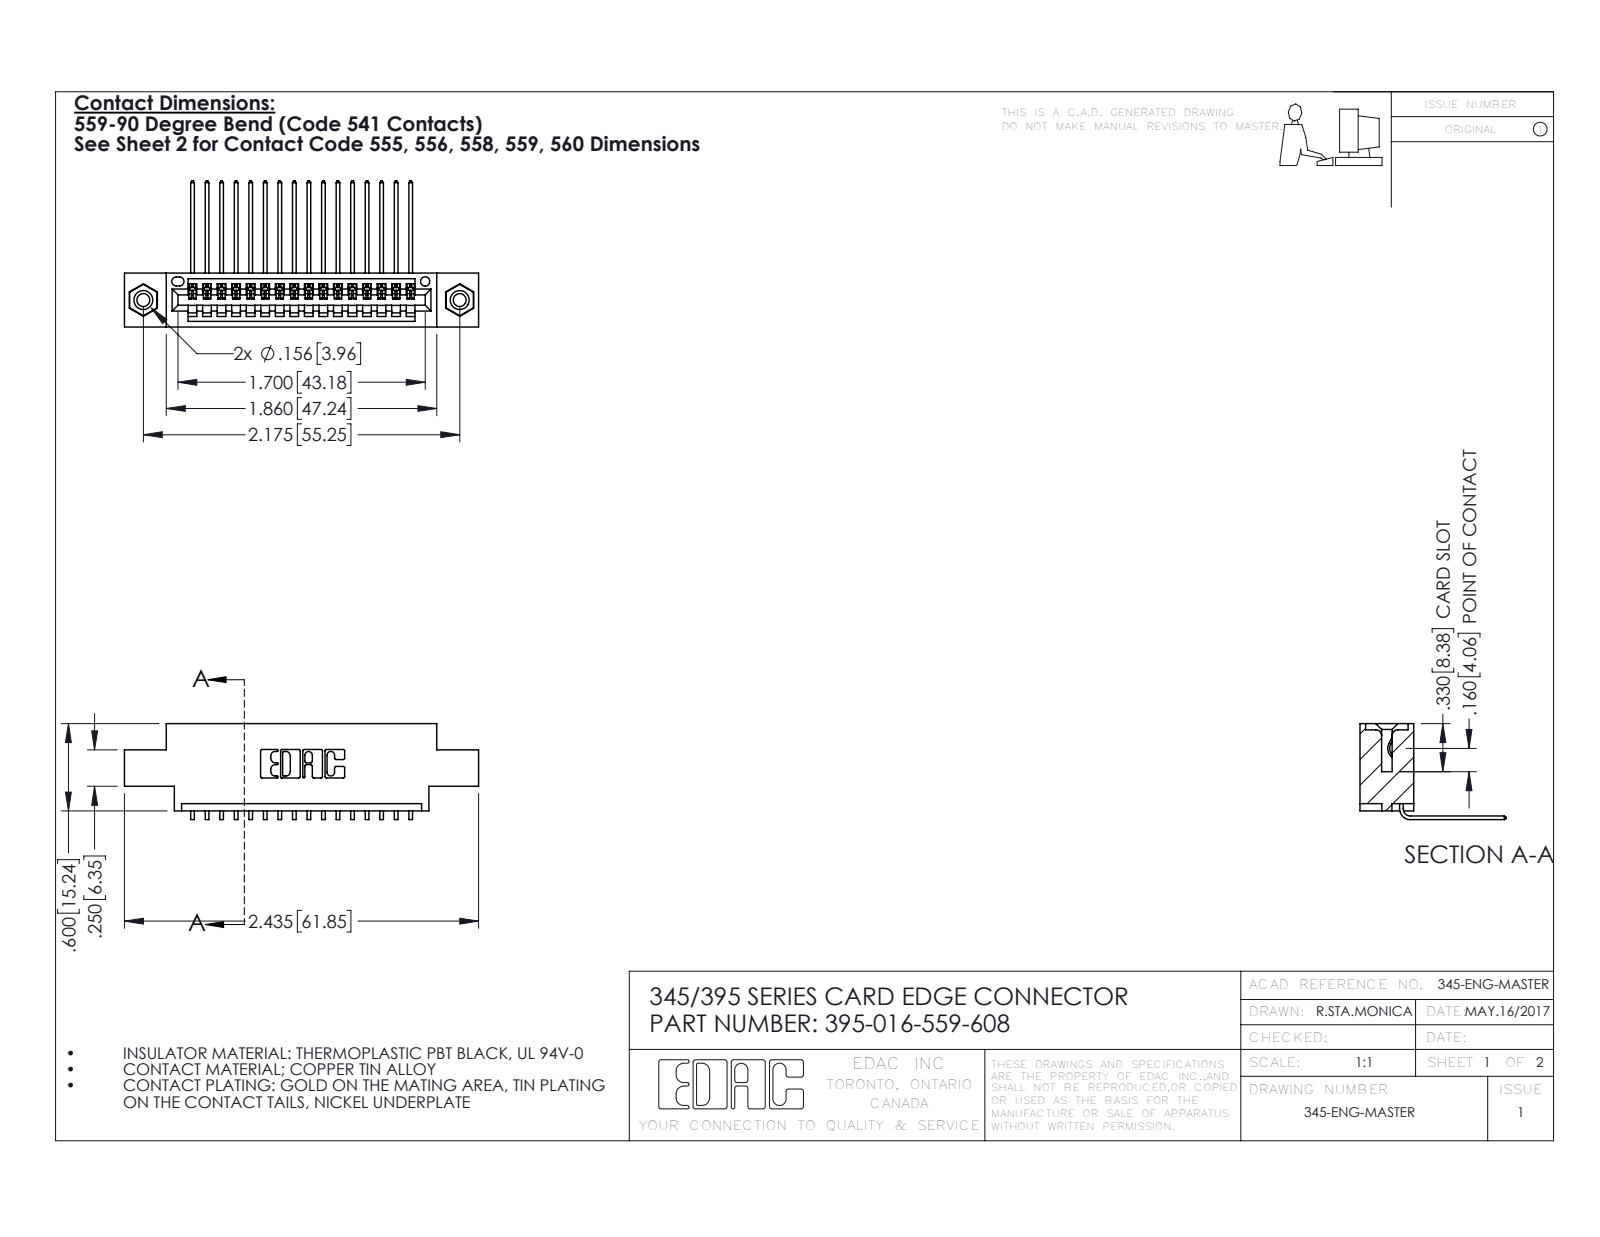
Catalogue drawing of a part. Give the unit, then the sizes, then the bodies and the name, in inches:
Units: inches
Overall size (bounding box): 2.435 × 1.005 × 0.659
Round holes (diameter × count): ⌀0.089 ×2, ⌀0.125 ×2, ⌀0.156 ×2, ⌀0.064 ×1
Round bosses / shafts (diameter × count): ⌀0.155 ×2
Partial cylindrical surfaces — rounded edges, fillets, slot ends (radius × count): R0.006 ×32, R0.01 ×22, R0.007 ×6, R0.031 ×6, R0.026 ×3, R0.031 ×2, R0.04 ×2, R0.014 ×1
Main face-to-face distances: 0.37, 0.072, 0.298, 0.2, 0.098, 0.272, 0.025, 0.1, 0.225, 0.15
Hole centre spacings: 0.27, 1.942, 2.175
Volume: 0.341 in³ · Surface area: 11.69 in²
Bodies: 19 solids, 1150 faces (788 planar, 346 cylindrical, 16 other)
Part name (STEP PRODUCT): 395-016-559-608; 345 Part_0.170 Offset - 0.156 Dia-TI; 345-292-001_558 559 Tail - 1; 345-250-001_345-250-003-102
STEP written by: SolidWorks 2016 (CONFIG_CONTROL_DESIGN)
